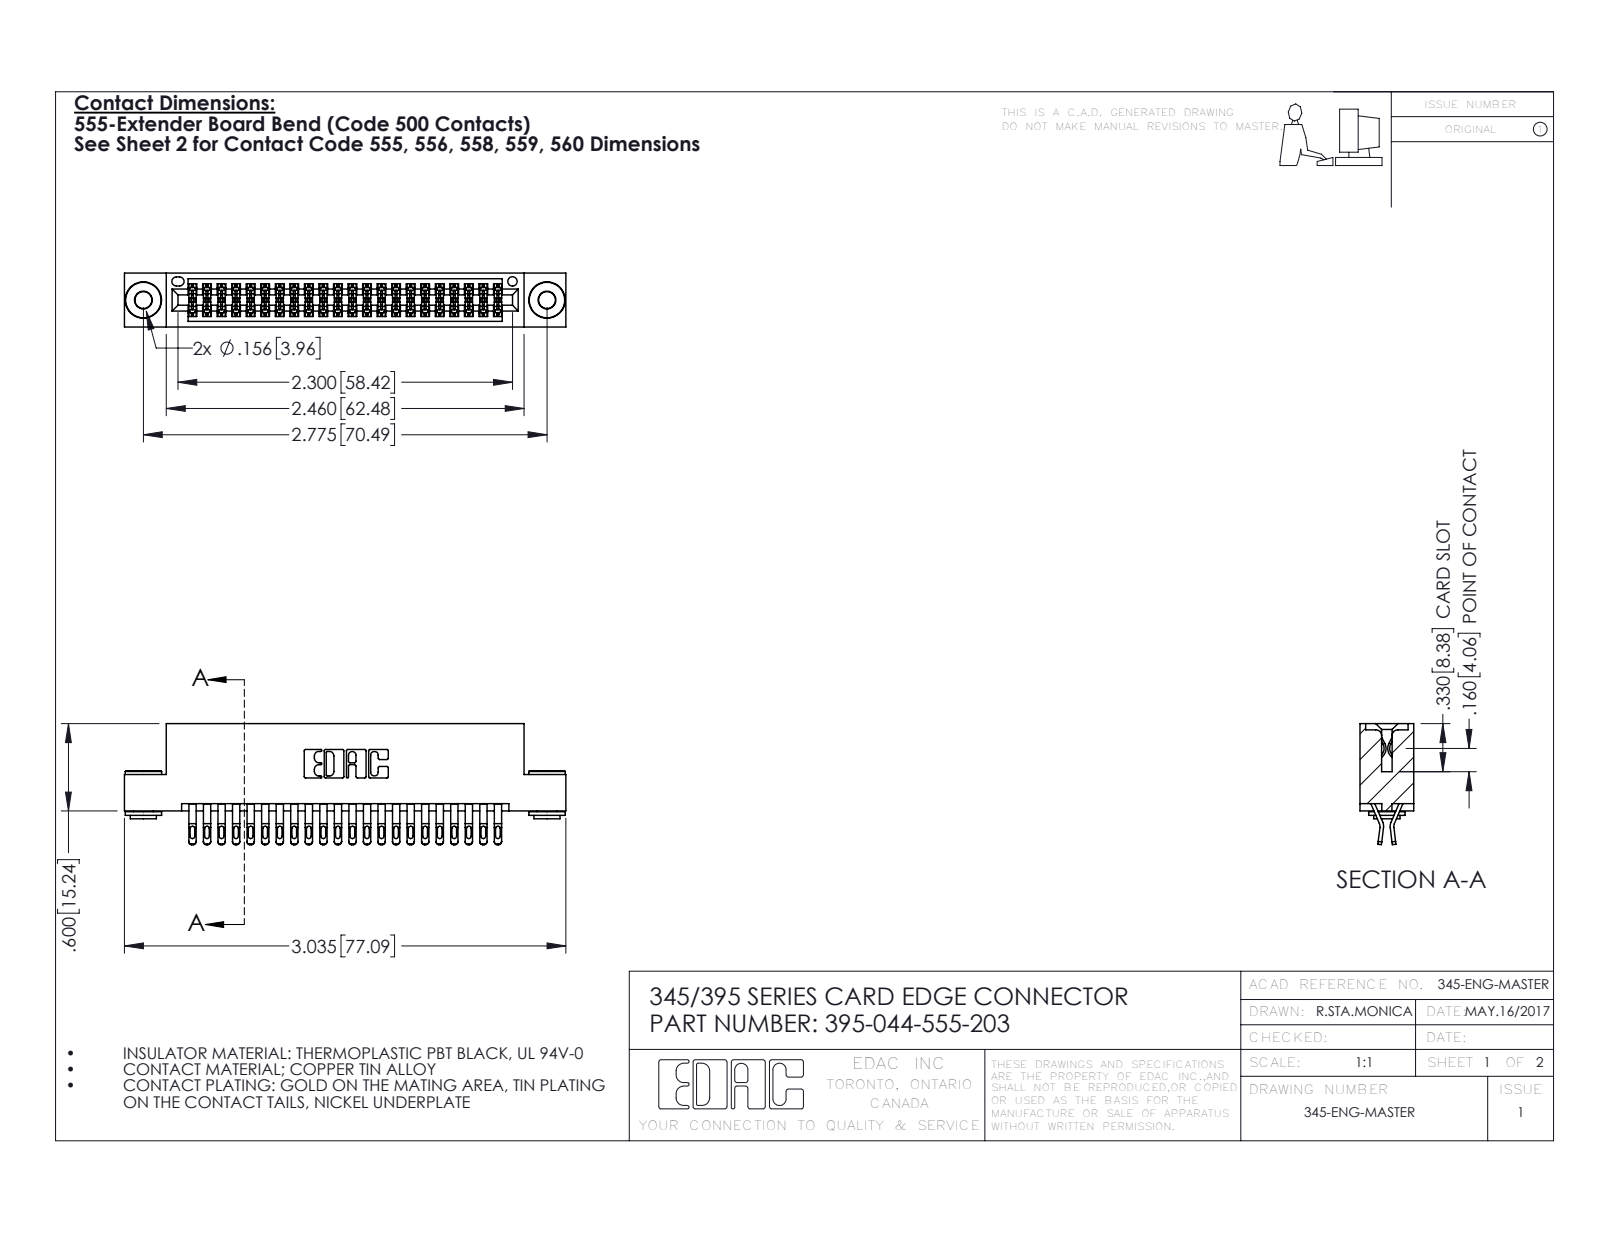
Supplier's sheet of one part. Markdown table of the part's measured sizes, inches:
| quantity | value |
| --- | --- |
| part name | 345-292-001_555 Tail; 345 Part_Flush Mounting Lugs - 0.156 Dia-TH; 345-250-002_345-250-002-102; 395-044-555-203 |
| STEP written by | SolidWorks 2016 (CONFIG_CONTROL_DESIGN) |
| units | inches |
| bodies | 47 solids, 2628 faces (1454 planar, 1166 cylindrical, 8 other) |
| overall size | 3.035 × 0.832 × 0.37 |
| volume | 0.455 in³ |
| surface area | 17.47 in² |
| round holes (diameter × count) | 0.116 × 2, 0.156 × 2, 0.064 × 1 |
| round bosses / shafts (diameter × count) | 0.25 × 2, 0.18 × 2, 0.136 × 2 |
| partial cylindrical surfaces (radius × count) | 0.016 × 110, 0.02 × 88, 0.006 × 66, 0.01 × 22, 0.007 × 6, 0.031 × 6, 0.026 × 3, 0.01 × 2 |
| main face-to-face distances | 0.072, 0.298, 0.2, 0.37, 0.025, 0.098, 0.272, 0.225, 0.175, 0.149 |
| hole center spacings | 0.27, 2.541, 2.775 |
